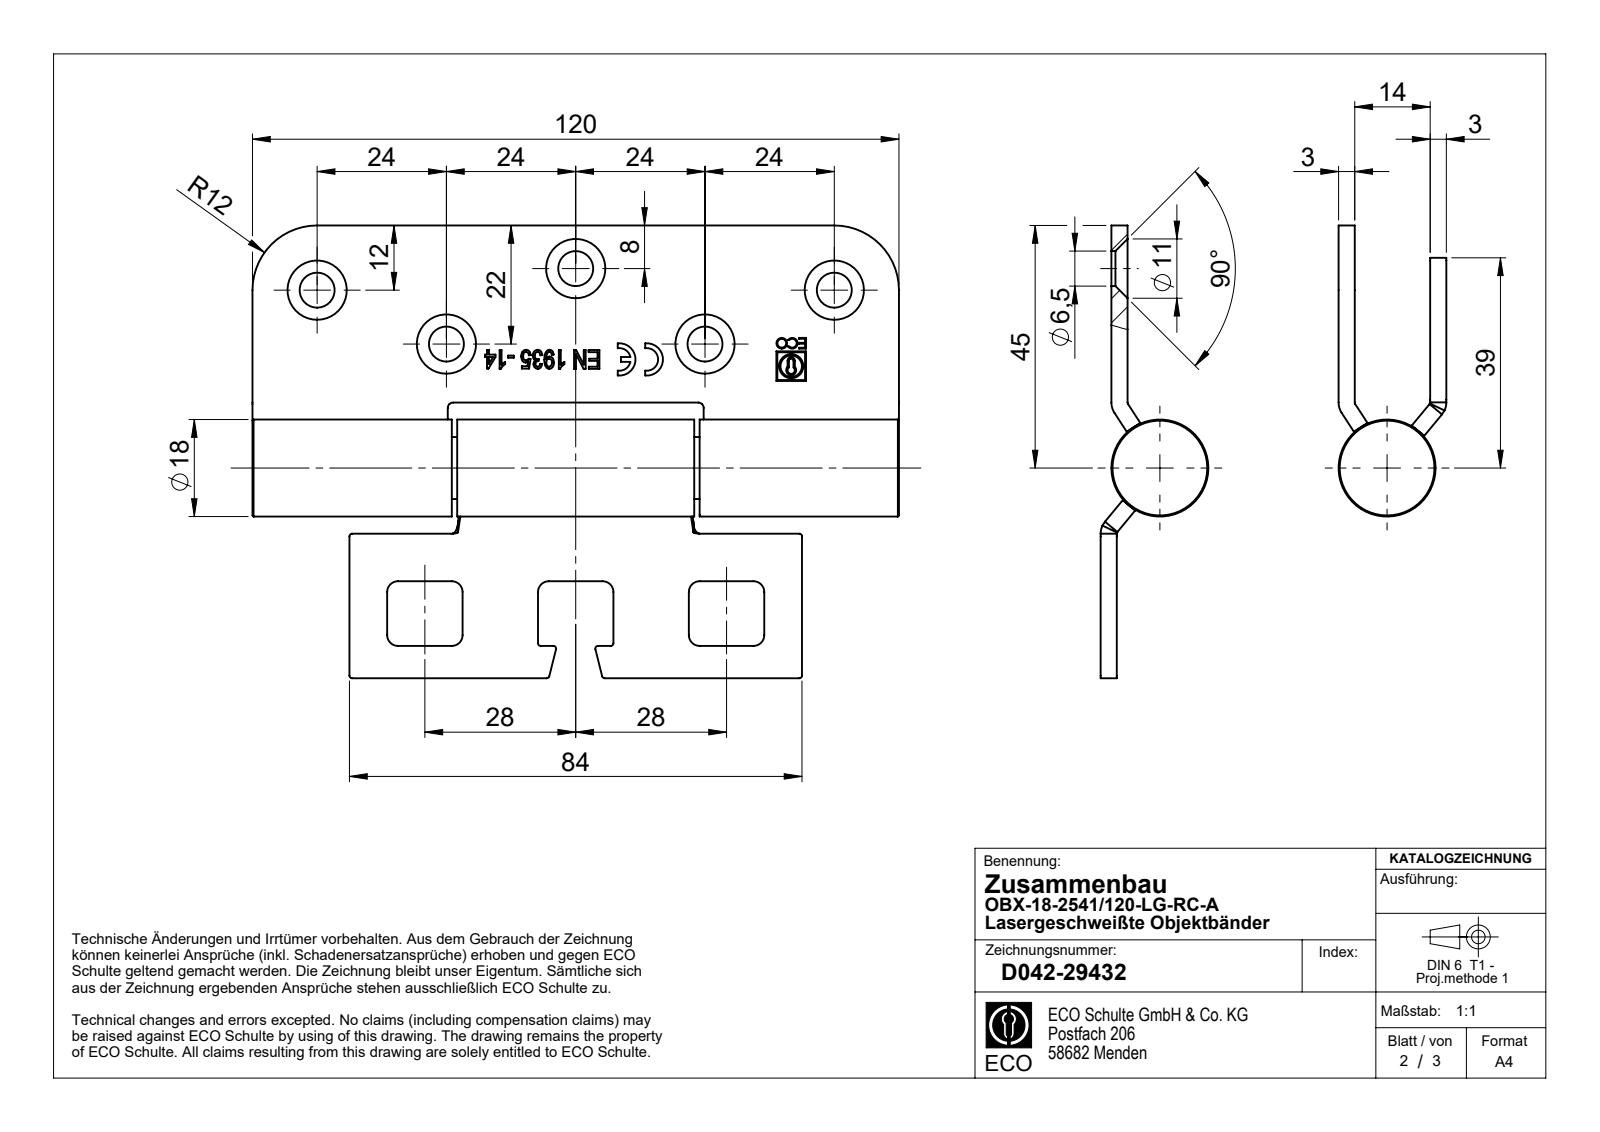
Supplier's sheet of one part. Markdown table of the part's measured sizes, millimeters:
| quantity | value |
| --- | --- |
| part name | D043-25259; D044-14308; DIN5401-III; D043-24264 (+4 more) |
| STEP written by | SolidWorks 2017 (AUTOMOTIVE_DESIGN) |
| units | millimeters |
| bodies | 11 solids, 453 faces (212 planar, 133 cylindrical, 108 other) |
| overall size | 120 × 54 × 20 |
| volume | 47 736 mm³ |
| surface area | 28 879 mm² |
| round holes (diameter × count) | 6.5 × 5, 2 × 2, 0.5 × 1, 4.5 × 1, 7.9 × 1 |
| round bosses / shafts (diameter × count) | 18 × 1, 12 × 1, 11.8 × 1, 11.5 × 1, 7.7 × 1, 4 × 1, 1.65 × 1 |
| partial cylindrical surfaces (radius × count) | 0.5 × 12, 2 × 10, 0.25 × 6, 0.68 × 2, 1 × 2, 2.1 × 2, 3 × 2, 3.5 × 2 |
| main face-to-face distances | 3, 17, 20, 14, 6, 82, 12, 11.5, 108.5, 120 |
| hole center spacings | 26, 27.78, 48.17, 72.69, 1.95, 4.25, 4.6, 12.56 |
